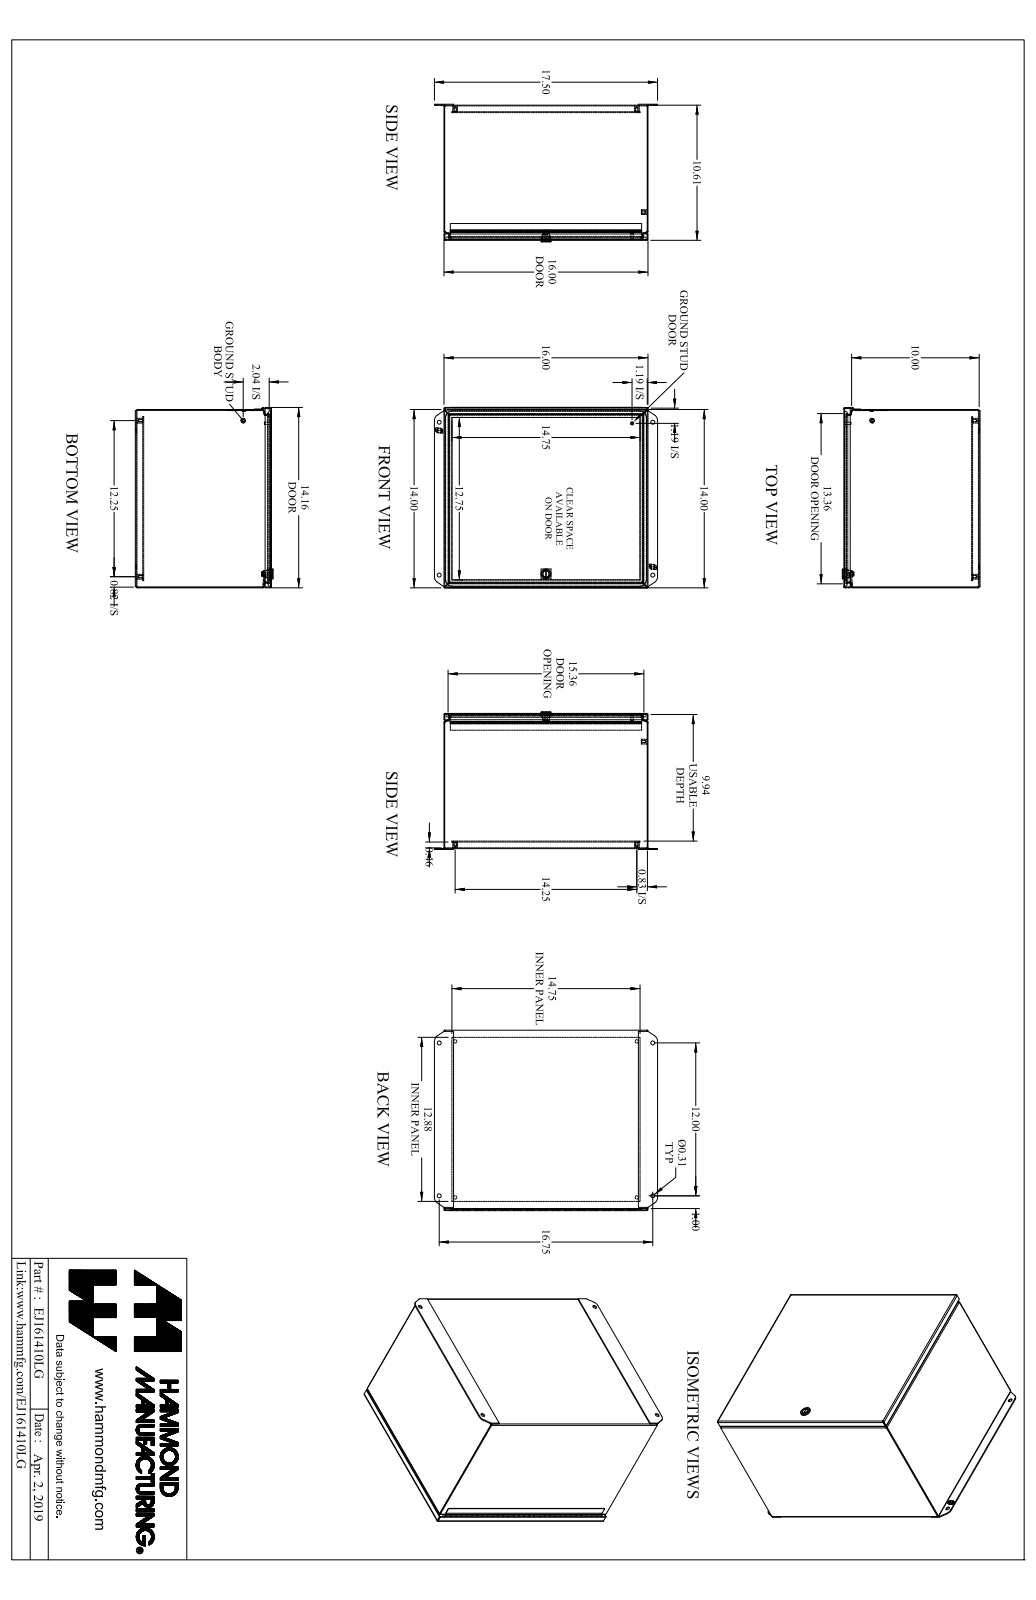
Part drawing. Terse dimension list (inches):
name: EJ161410LG_Default
written by: SolidWorks 2019 (CONFIG_CONTROL_DESIGN)
unit: in
bodies: 16 solids, 771 faces (425 planar, 254 cylindrical, 92 other)
size: 17.5 × 14.165 × 10.805
volume: 86.44 in³; area: 2 880 in²
holes: 5× ⌀0.156, 4× ⌀0.265, 4× ⌀0.313, 1× ⌀0.05, 1× ⌀0.516
bosses: 5× ⌀0.375, 1× ⌀0.788, 1× ⌀0.535, 1× ⌀0.496, 1× ⌀0.435, 1× ⌀0.25, 1× ⌀0.188, 1× ⌀0.1
rounds: 16× R0.029, 16× R0.086, 10× R0.281, 4× R0.25, 4× R0.499, 4× R0.5, 2× R0.06, 2× R0.539
face distances: 0.057, 10.554, 13.943, 15.943, 0.072, 0.589, 10.611, 10.497, 0.46, 0.517
hole spacings: 1.256, 15.5, 19.679, 14.25, 12.189, 7.128, 8.375, 12
